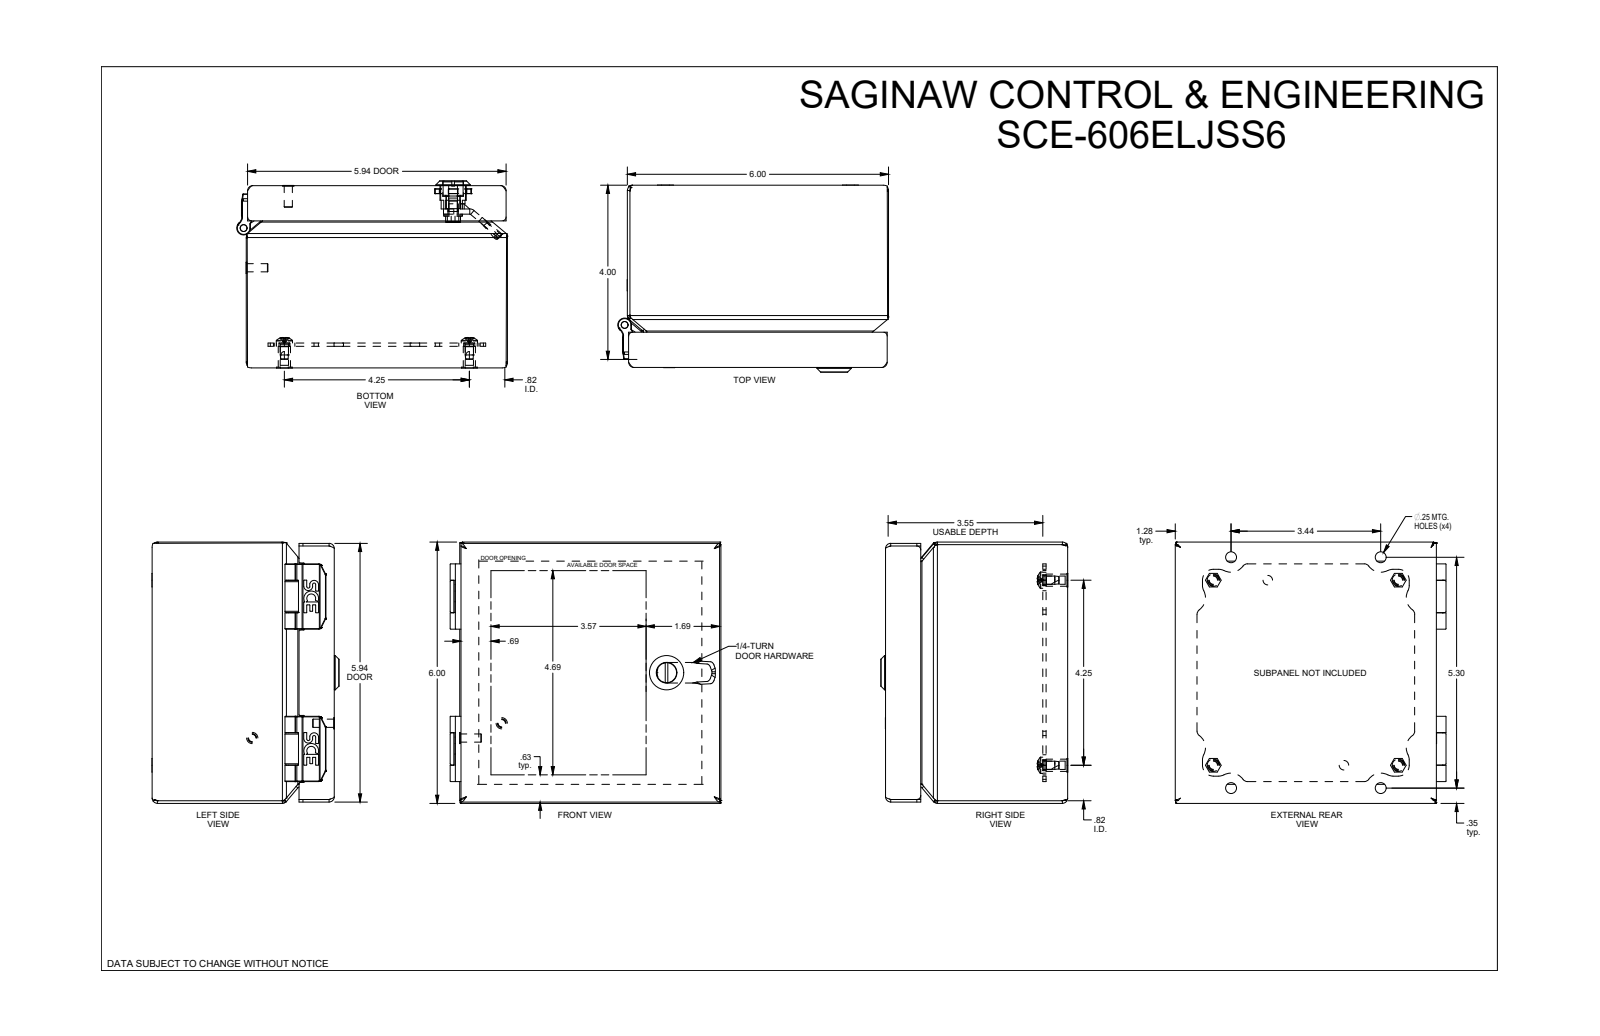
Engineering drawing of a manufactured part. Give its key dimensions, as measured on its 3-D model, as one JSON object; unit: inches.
{"part_name": "SCE-606ELJSS6", "step_written_by": "SolidWorks 2019 (CONFIG_CONTROL_DESIGN)", "units": "inches", "bodies": {"solids": 0, "faces": 2717, "planar": 863, "cylindrical": 790, "other": 1064}, "overall_size": [6.22, 6, 4.296], "round_holes": [[0.25, 8], [0.19, 4], [0.284, 4], [0.479, 4], [0.02, 2], [0.1, 2], [0.174, 2], [0.196, 2], [0.218, 2], [0.266, 2], [0.158, 1], [0.2, 1]], "round_bosses_or_shafts": [[0.188, 6], [0.373, 4], [0.28, 4], [0.17, 4], [0.16, 4], [0.135, 4], [0.108, 4], [0.26, 2]], "partial_cylinders_radius": [[0.106, 132], [0.005, 131], [0.008, 32], [0.008, 26], [0.025, 24], [0.03, 24], [0.12, 23], [0.06, 22]], "face_to_face_distances": [0.06, 5.94, 0.06, 5.88, 6, 4.124, 4.065, 4.185, 4.125, 0.571], "hole_center_spacings": [0.664, 3.88, 4.25, 4.792, 6.13, 0.994, 1.25, 2.157]}
